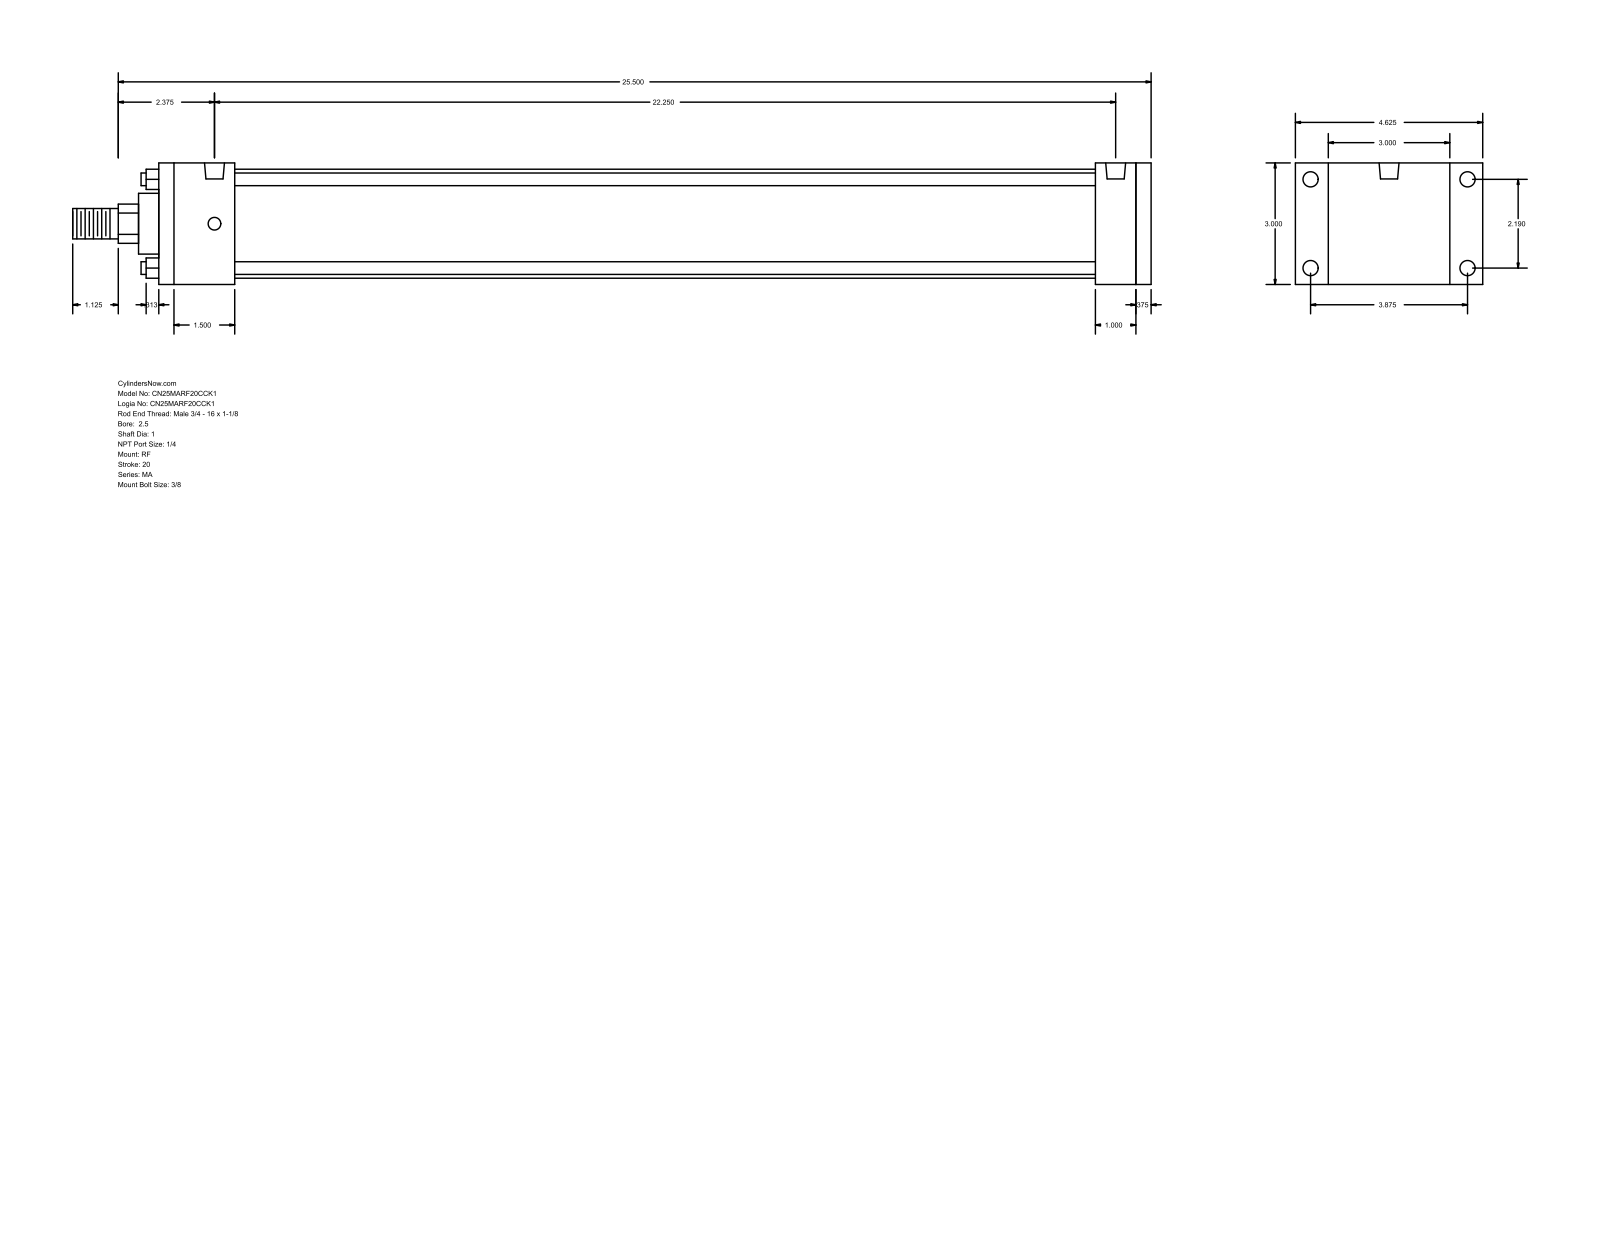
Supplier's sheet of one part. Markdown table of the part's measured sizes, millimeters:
| quantity | value |
| --- | --- |
| part name | MA_RF__0250_1 |
| STEP written by | GSSL Pune (CONFIG_CONTROL_DESIGN) |
| units | millimeters |
| bodies | 0 solids, 92 faces (64 planar, 28 cylindrical, 0 other) |
| overall size | 676.27 × 117.47 × 76.2 |
| round holes (diameter × count) | 7.94 × 4, 9.53 × 4, 12.49 × 2 |
| round bosses / shafts (diameter × count) | 7.94 × 4, 68.33 × 1, 38.1 × 1, 25.4 × 1, 19.05 × 1 |
| partial cylindrical surfaces (radius × count) | 12.29 × 1 |
| main face-to-face distances | 76.2, 622.3, 612.77, 9.53, 25.4, 47.63, 587.37, 539.74, 565.14, 574.67 |
| hole center spacings | 55.62, 98.42, 113.05, 565.15 |
